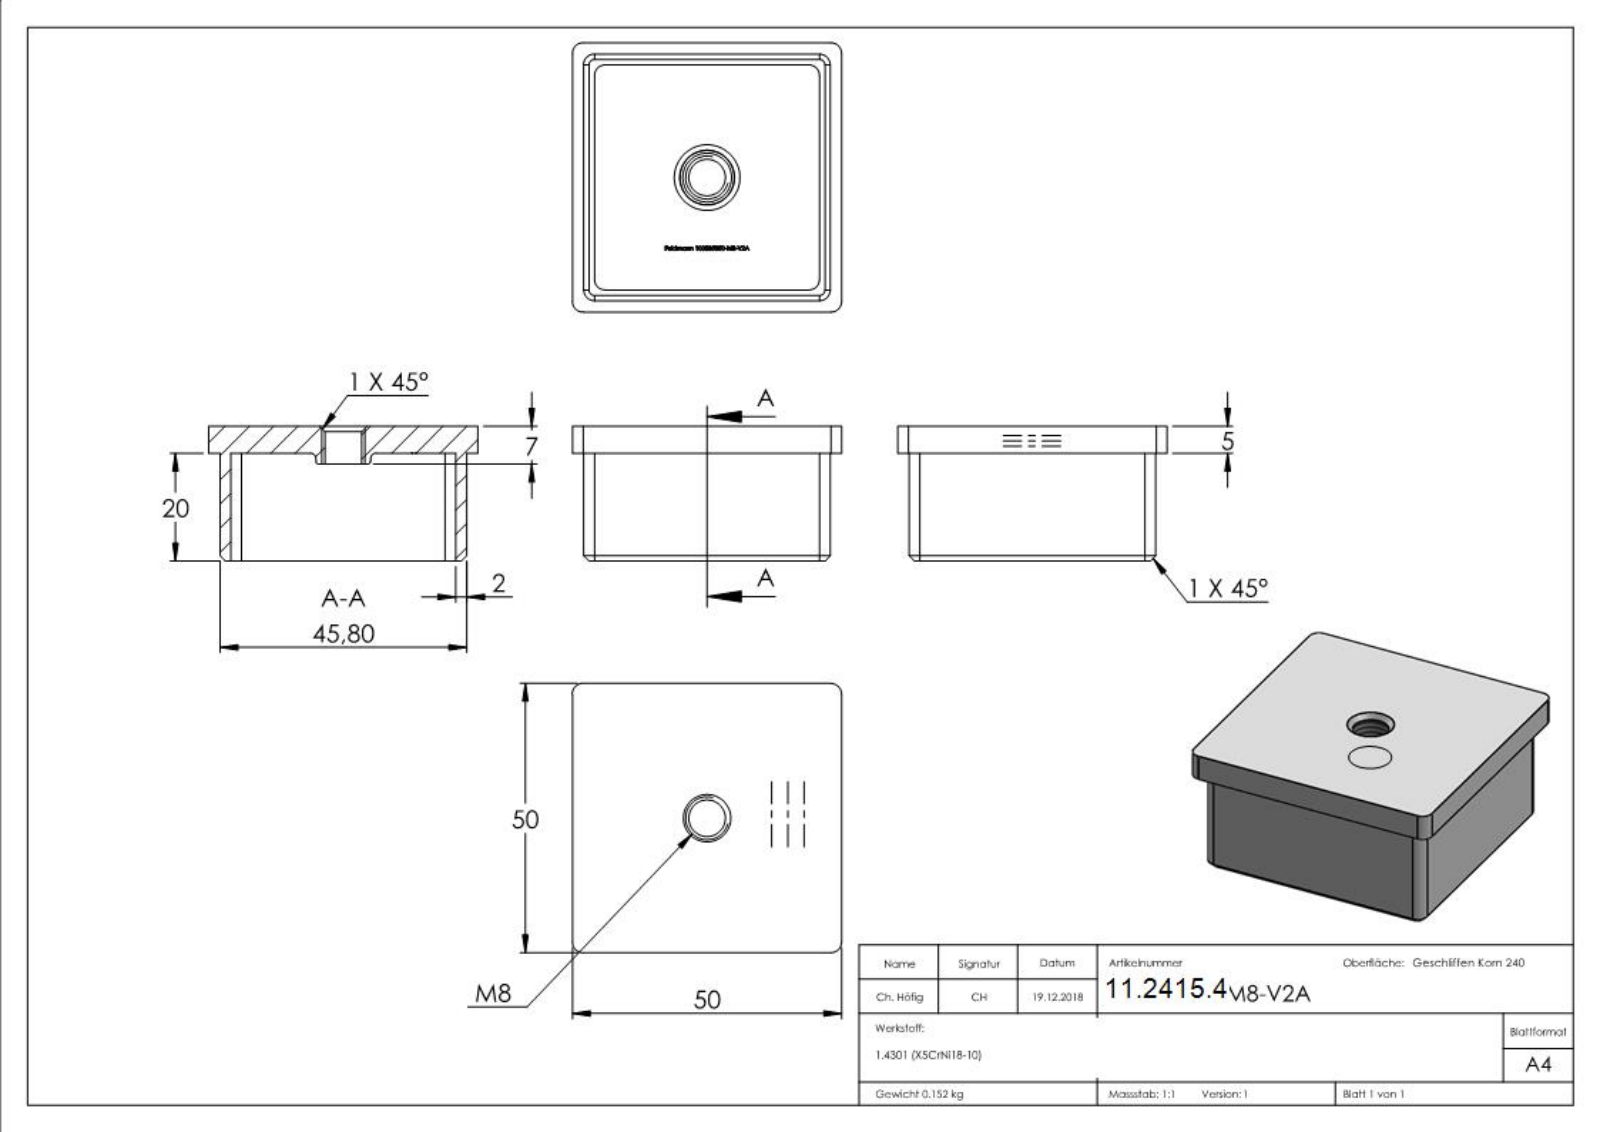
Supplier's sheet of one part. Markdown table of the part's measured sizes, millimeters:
| quantity | value |
| --- | --- |
| part name | 100035050-M8-V2A |
| STEP written by | SolidWorks 2015 (CONFIG_CONTROL_DESIGN) |
| units | millimeters |
| bodies | 1 solid, 348 faces (176 planar, 14 cylindrical, 158 other) |
| overall size | 50 × 50 × 25 |
| volume | 19 303 mm³ |
| surface area | 12 856 mm² |
| round holes (diameter × count) | 6.8 × 1 |
| partial cylindrical surfaces (radius × count) | 2 × 12 |
| main face-to-face distances | 2, 43.8, 5, 45.8, 41.8, 2.1, 4.1, 45.9, 47.9, 50 |
